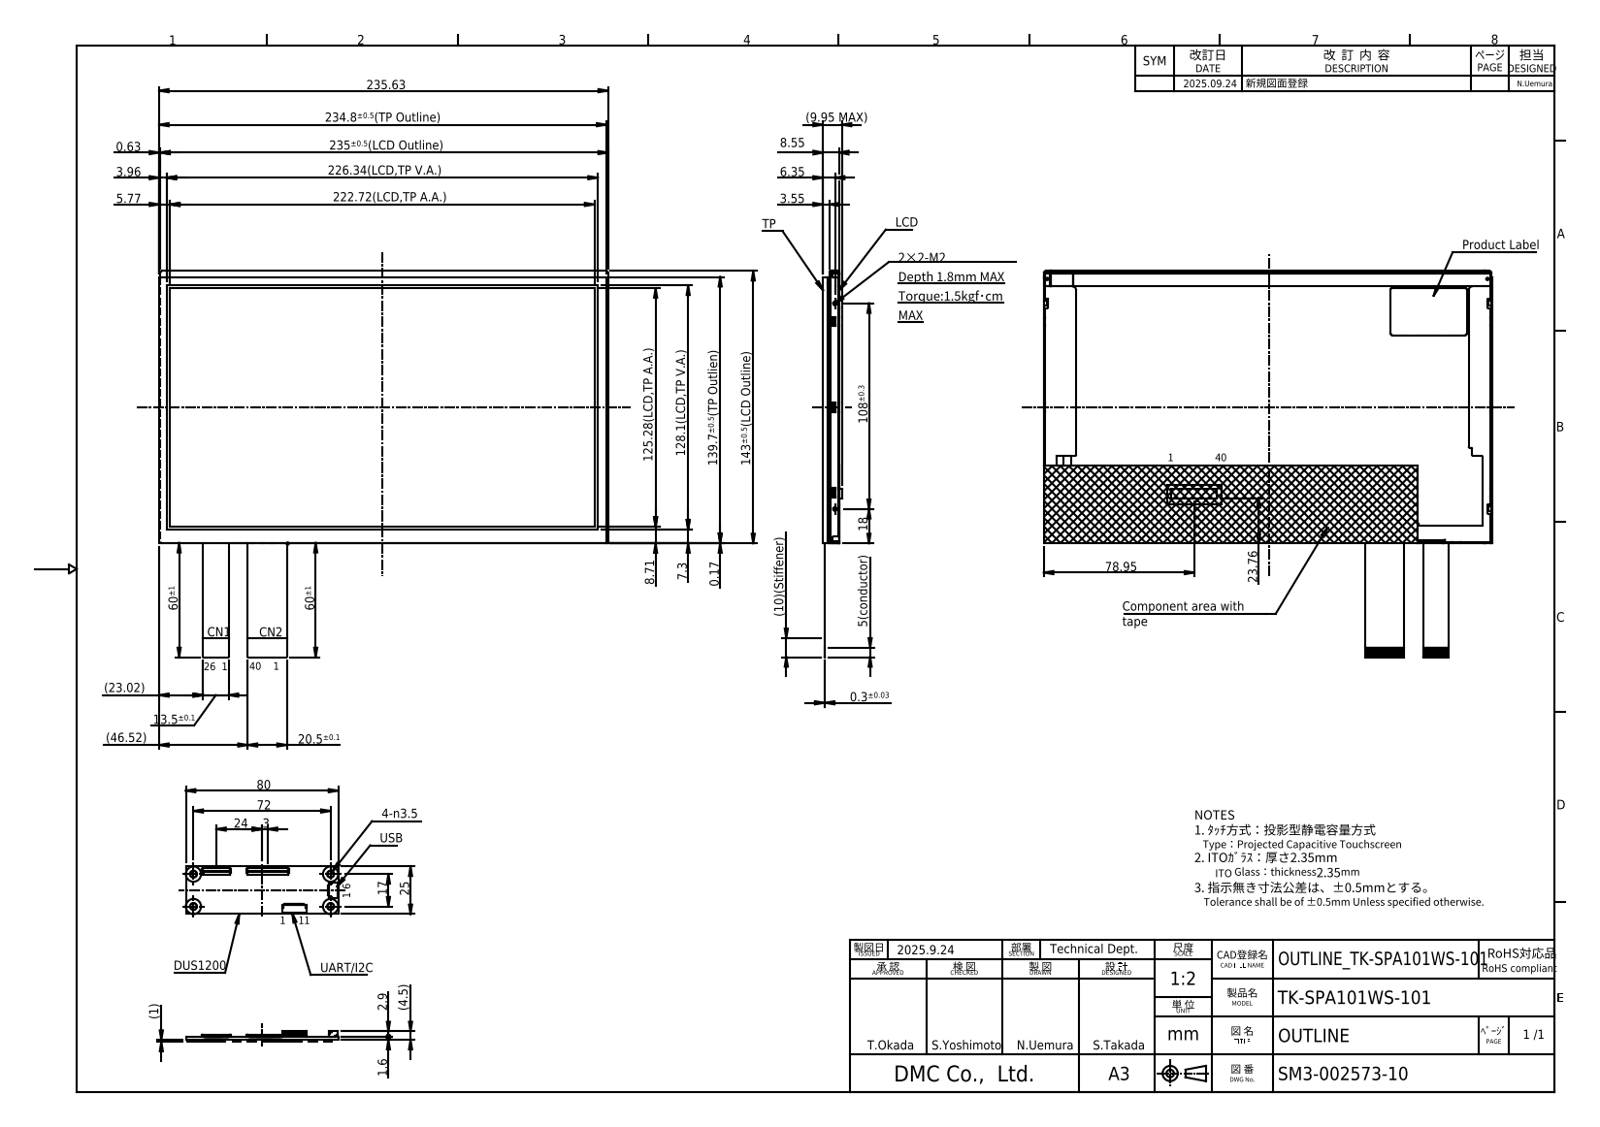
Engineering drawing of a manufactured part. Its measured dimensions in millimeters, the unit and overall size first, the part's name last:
Units: millimetres
Overall size (bounding box): 235.63 × 202.83 × 9.95
Round holes (diameter × count): ⌀1.3 ×2, ⌀2 ×2
Round bosses / shafts (diameter × count): ⌀2.6 ×2, ⌀0.8 ×1
Partial cylindrical surfaces — rounded edges, fillets, slot ends (radius × count): R0.3 ×28, R0.5 ×14, R0.1 ×8, R1 ×8, R0.25 ×7, R0.2 ×6, R0.6 ×4, R0.7 ×4
Main face-to-face distances: 3.98, 2.35, 1.26, 1.63, 2.89, 5.24, 3.33, 4.59, 3.38, 4.64
Hole centre spacings: 108, 231.08
Volume: 183 711 mm³ · Surface area: 251 190 mm²
Bodies: 2 solids, 1088 faces (963 planar, 115 cylindrical, 10 other)
Part name (STEP PRODUCT): HP_TK-SPA101WS-101
STEP written by: Autodesk Inventor 2024 (AUTOMOTIVE_DESIGN)
